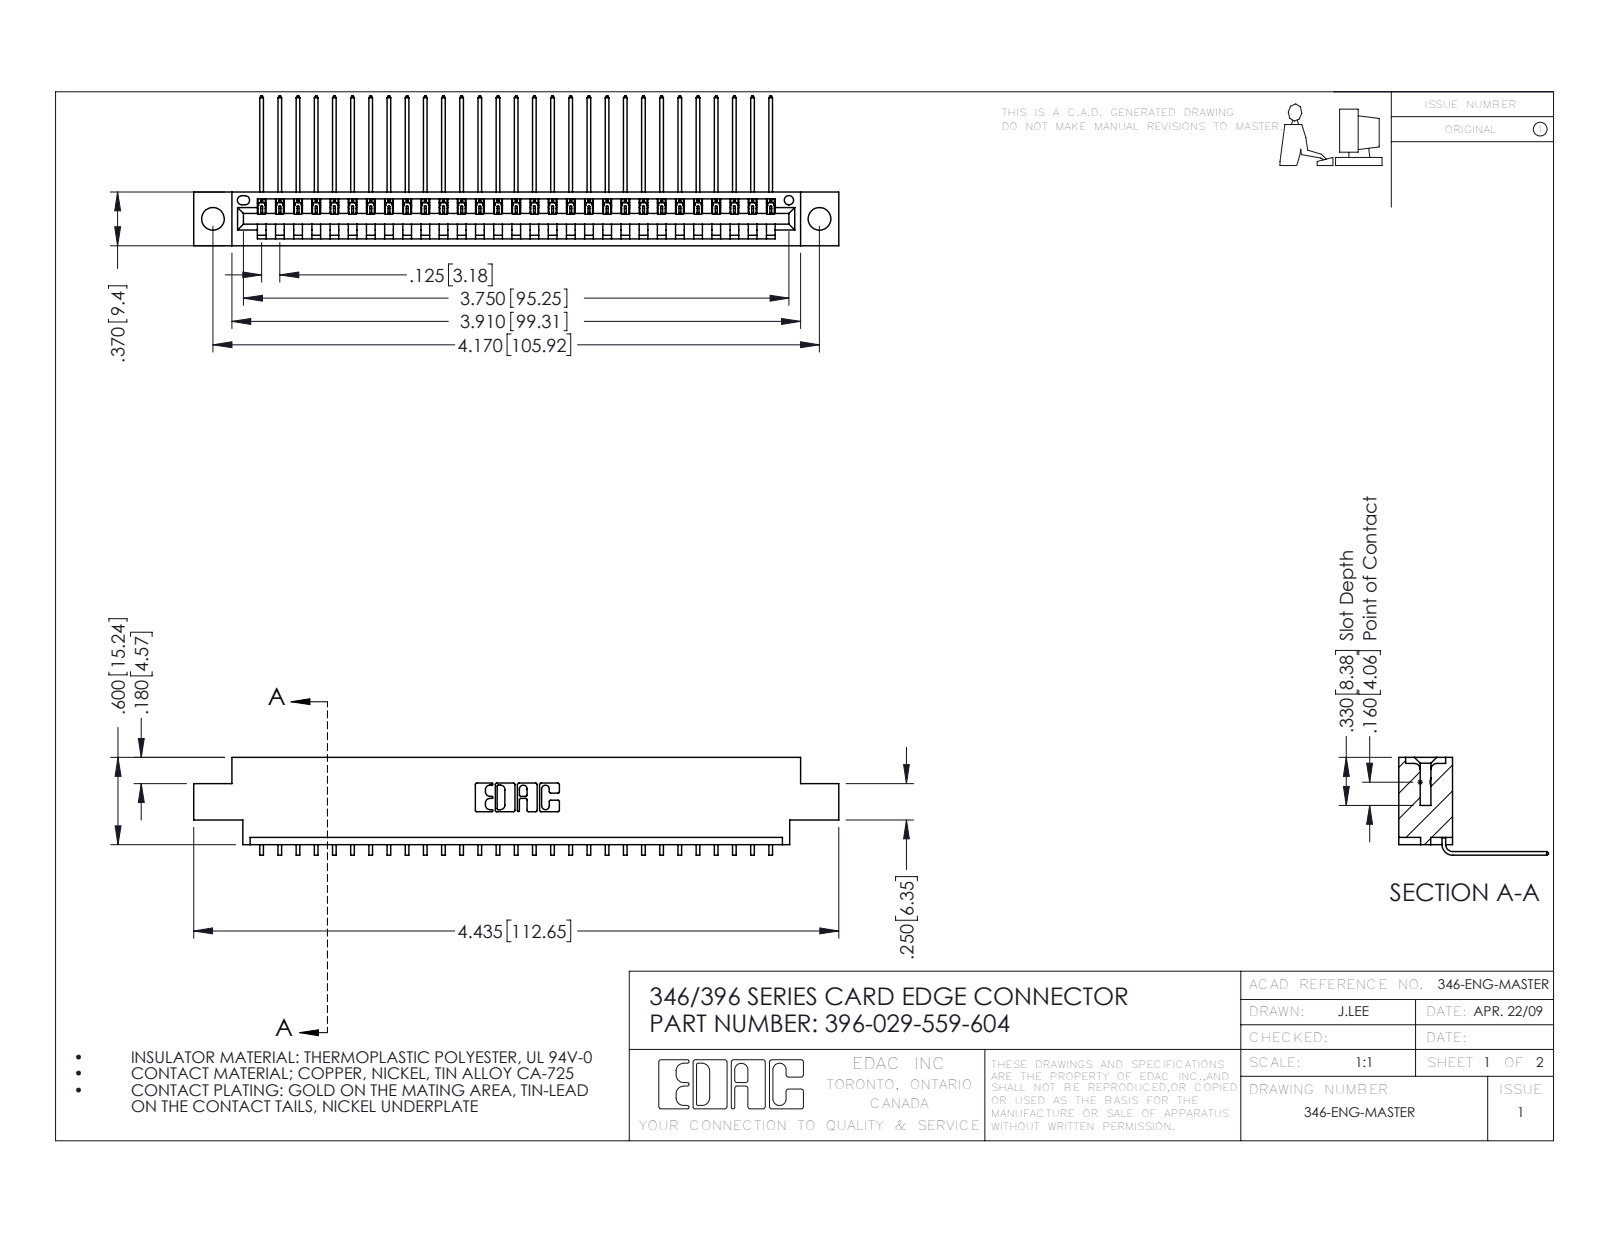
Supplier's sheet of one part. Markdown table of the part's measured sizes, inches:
| quantity | value |
| --- | --- |
| part name | 346 Part_0.170 Offset - 0.156 Dia-TH; 345-292-001_558 559 Tail - 1; 396-029-559-604 |
| STEP written by | SolidWorks 2016 (CONFIG_CONTROL_DESIGN) |
| units | inches |
| bodies | 30 solids, 1866 faces (1298 planar, 568 cylindrical, 0 other) |
| overall size | 4.435 × 1.03 × 0.673 |
| volume | 0.644 in³ |
| surface area | 21.06 in² |
| round holes (diameter × count) | 0.156 × 2, 0.064 × 1 |
| partial cylindrical surfaces (radius × count) | 0.006 × 58, 0.01 × 22, 0.007 × 6, 0.031 × 6, 0.026 × 3, 0.031 × 2, 0.04 × 2, 0.014 × 1 |
| main face-to-face distances | 0.048, 0.322, 0.37, 0.25, 0.025, 0.072, 0.148, 0.222, 0.1, 0.174 |
| hole center spacings | 0.246, 3.962, 4.17 |
